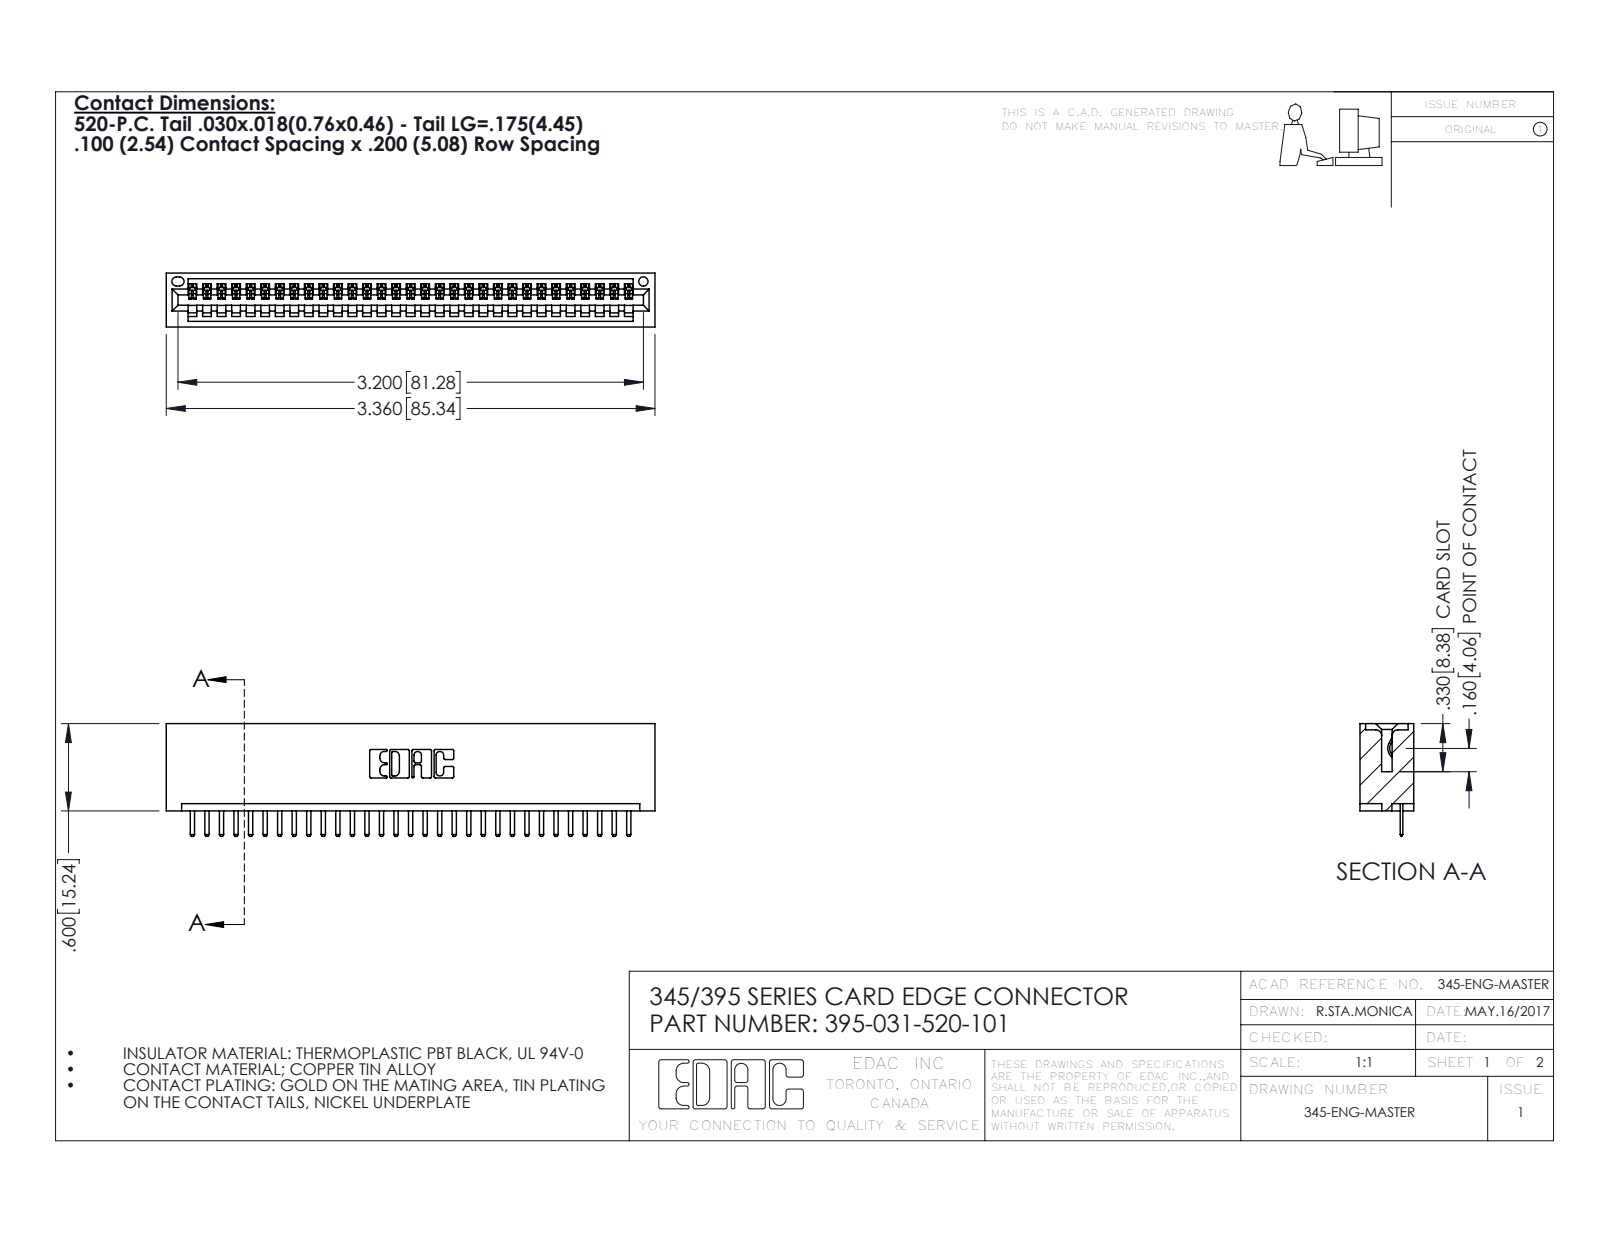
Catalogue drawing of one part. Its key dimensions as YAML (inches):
part_name: "345 Part_No Mounting Lugs; 345-292-001_345-293-120; 395-031-520-101"
step_written_by: "SolidWorks 2016 (CONFIG_CONTROL_DESIGN)"
units: inches
bodies: {solids: 32, faces: 2040, planar: 1378, cylindrical: 662, other: 0}
overall_size: [3.36, 0.775, 0.37]
volume: 0.519
surface_area: 17.14
round_holes:
  - {diameter: 0.064, count: 1}
partial_cylinders:
  - {radius: 0.01, count: 64}
  - {radius: 0.006, count: 62}
  - {radius: 0.01, count: 22}
  - {radius: 0.007, count: 6}
  - {radius: 0.031, count: 6}
  - {radius: 0.026, count: 3}
  - {radius: 0.031, count: 2}
  - {radius: 0.04, count: 2}
face_to_face_distances: [0.298, 0.072, 0.37, 0.2, 0.098, 0.272, 0.025, 0.225, 0.072, 0.149]
